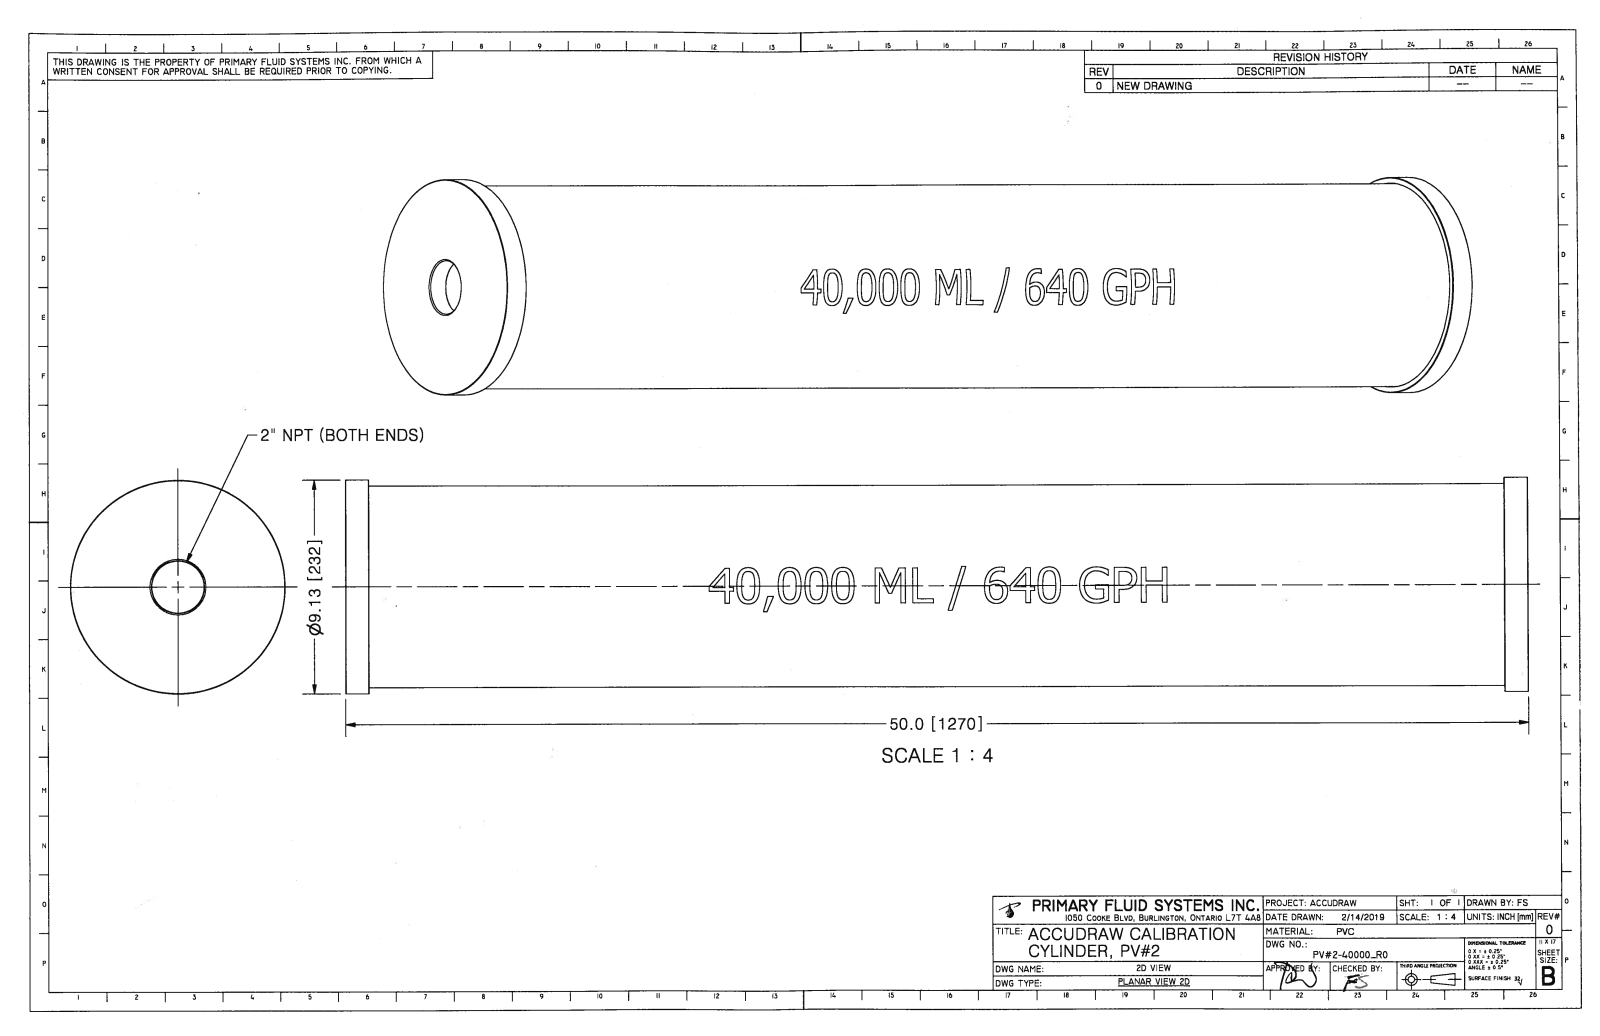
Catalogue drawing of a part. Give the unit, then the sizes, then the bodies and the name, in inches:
Units: inches
Overall size (bounding box): 50 × 9.125 × 9.125
Round holes (diameter × count): ⌀8.255 ×1, ⌀8.654 ×1
Round bosses / shafts (diameter × count): ⌀9.125 ×1, ⌀8.599 ×1, ⌀8.217 ×1
Partial cylindrical surfaces — rounded edges, fillets, slot ends (radius × count): R4.299 ×1
Main face-to-face distances: 50, 49, 1, 48, 0.5, 49.5, 48.5, 0.199, 11.032, 9.639
Volume: 334.1 in³ · Surface area: 2 952 in²
Bodies: 1 solid, 239 faces (82 planar, 32 cylindrical, 125 other)
STEP written by: Autodesk Inventor 2009 (AUTOMOTIVE_DESIGN)
